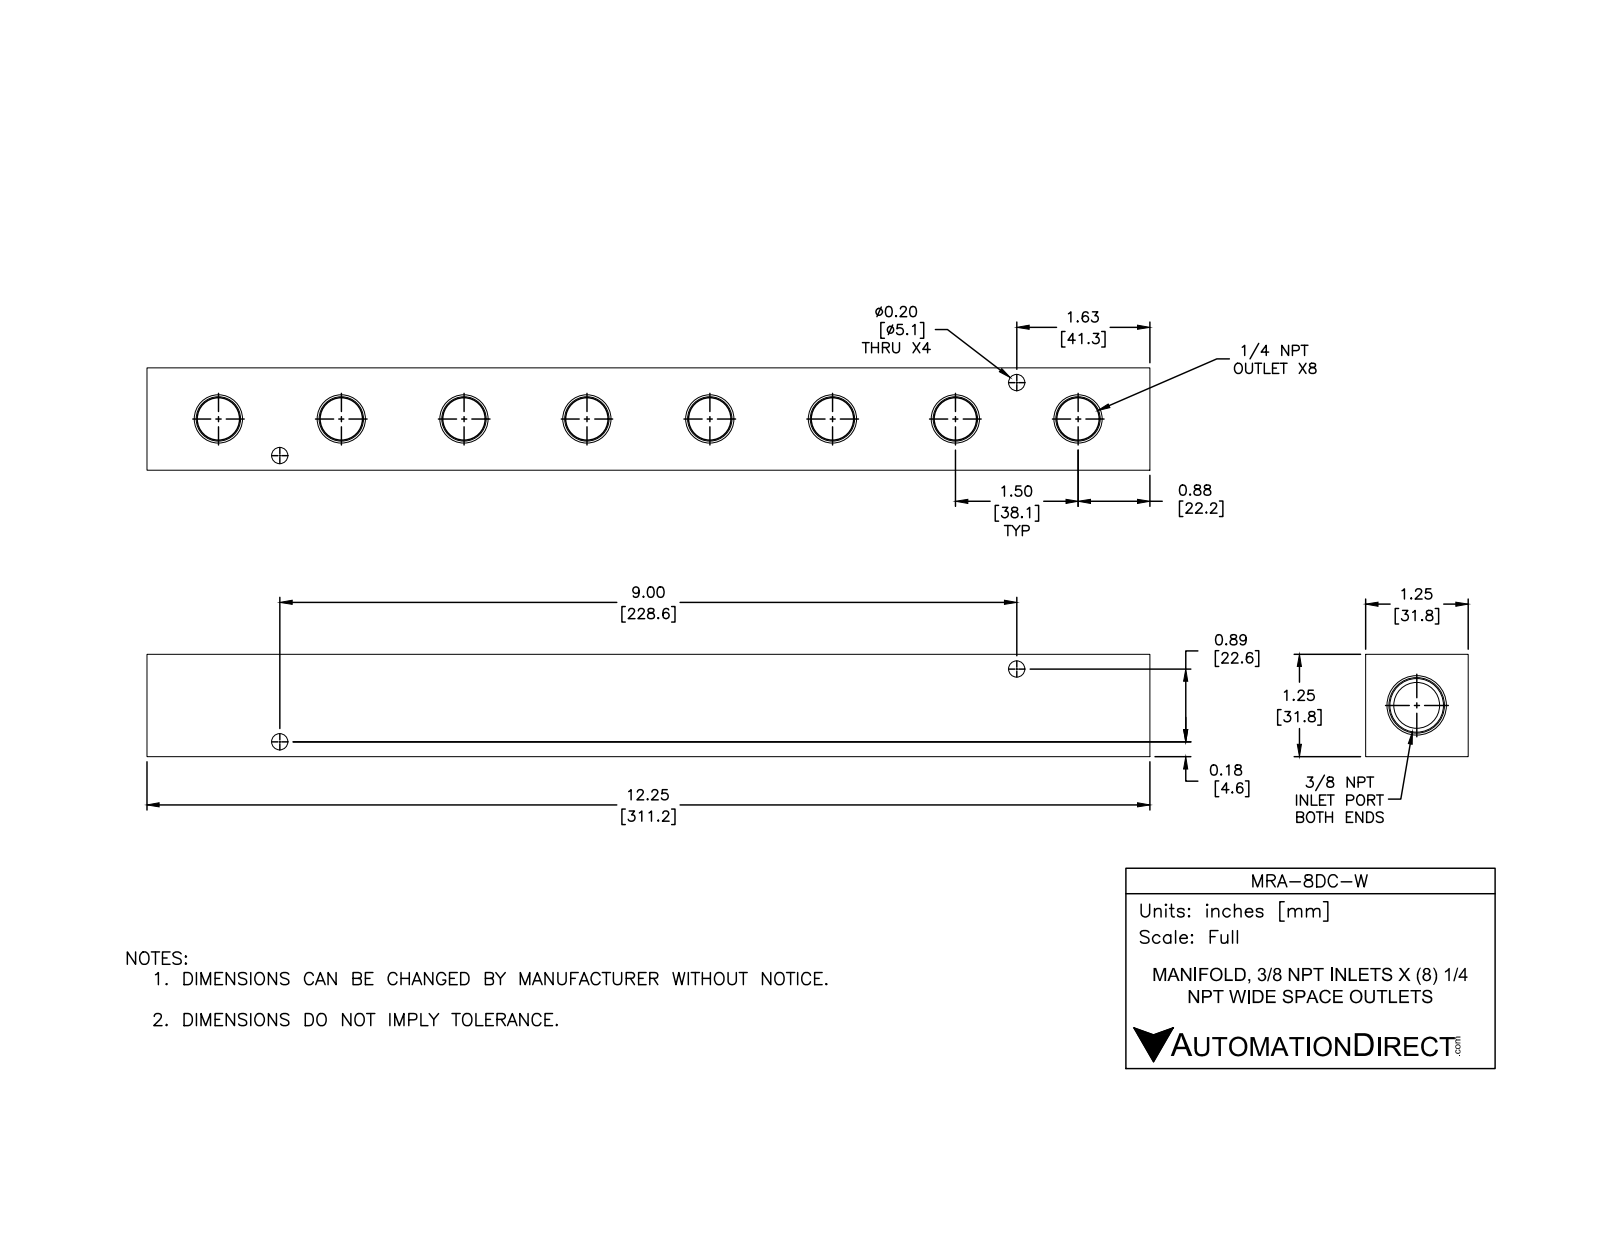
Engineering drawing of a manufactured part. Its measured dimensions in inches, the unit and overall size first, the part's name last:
Units: inches
Overall size (bounding box): 12.25 × 1.25 × 1.25
Round holes (diameter × count): ⌀0.2 ×4, ⌀0.562 ×1
Partial cylindrical surfaces — rounded edges, fillets, slot ends (radius × count): R0.219 ×8
Main face-to-face distances: 1.25, 12.25, 0.86, 0.39, 0.41, 11.84, 11.43
Hole centre spacings: 9.044
Volume: 15.22 in³ · Surface area: 90.15 in²
Bodies: 1 solid, 98 faces (24 planar, 34 cylindrical, 40 other)
Part name (STEP PRODUCT): MRA-8DC-W
STEP written by: SolidWorks 2015 (CONFIG_CONTROL_DESIGN)
